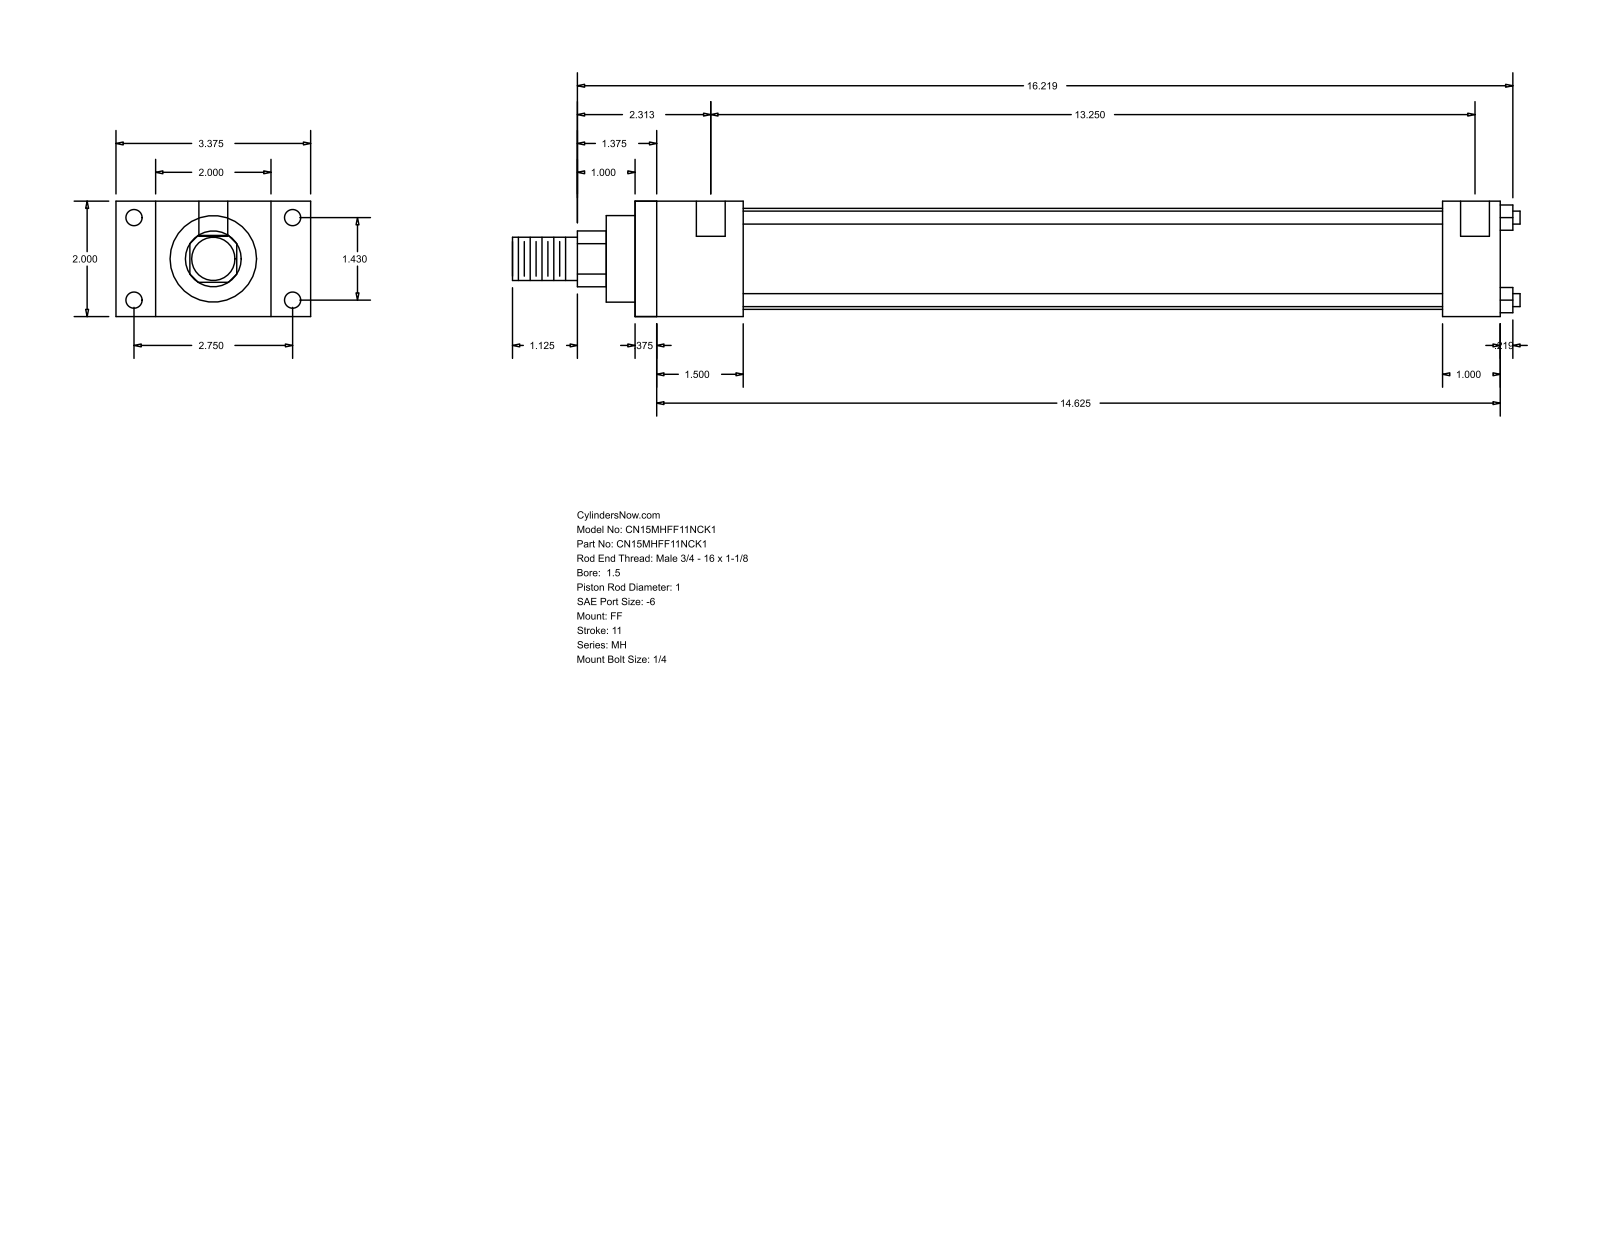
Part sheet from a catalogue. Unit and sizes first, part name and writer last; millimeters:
Units: millimetres
Overall size (bounding box): 443.71 × 85.72 × 50.8
Round holes (diameter × count): ⌀5.56 ×4, ⌀7.14 ×4, ⌀12.7 ×2
Round bosses / shafts (diameter × count): ⌀5.71 ×4, ⌀44.45 ×1, ⌀38.1 ×1, ⌀25.4 ×1, ⌀19.05 ×1
Partial cylindrical surfaces — rounded edges, fillets, slot ends (radius × count): R12.29 ×1
Main face-to-face distances: 50.8, 381, 9.52, 371.48, 25.4, 17.46, 68.26, 47.63, 38.11, 333.37
Hole centre spacings: 36.32, 69.84, 78.72, 339.73, 3.18, 336.55
Bodies: 0 solids, 92 faces (64 planar, 28 cylindrical, 0 other)
Part name (STEP PRODUCT): MH_FF__0150_1
STEP written by: GSSL Pune (CONFIG_CONTROL_DESIGN)
